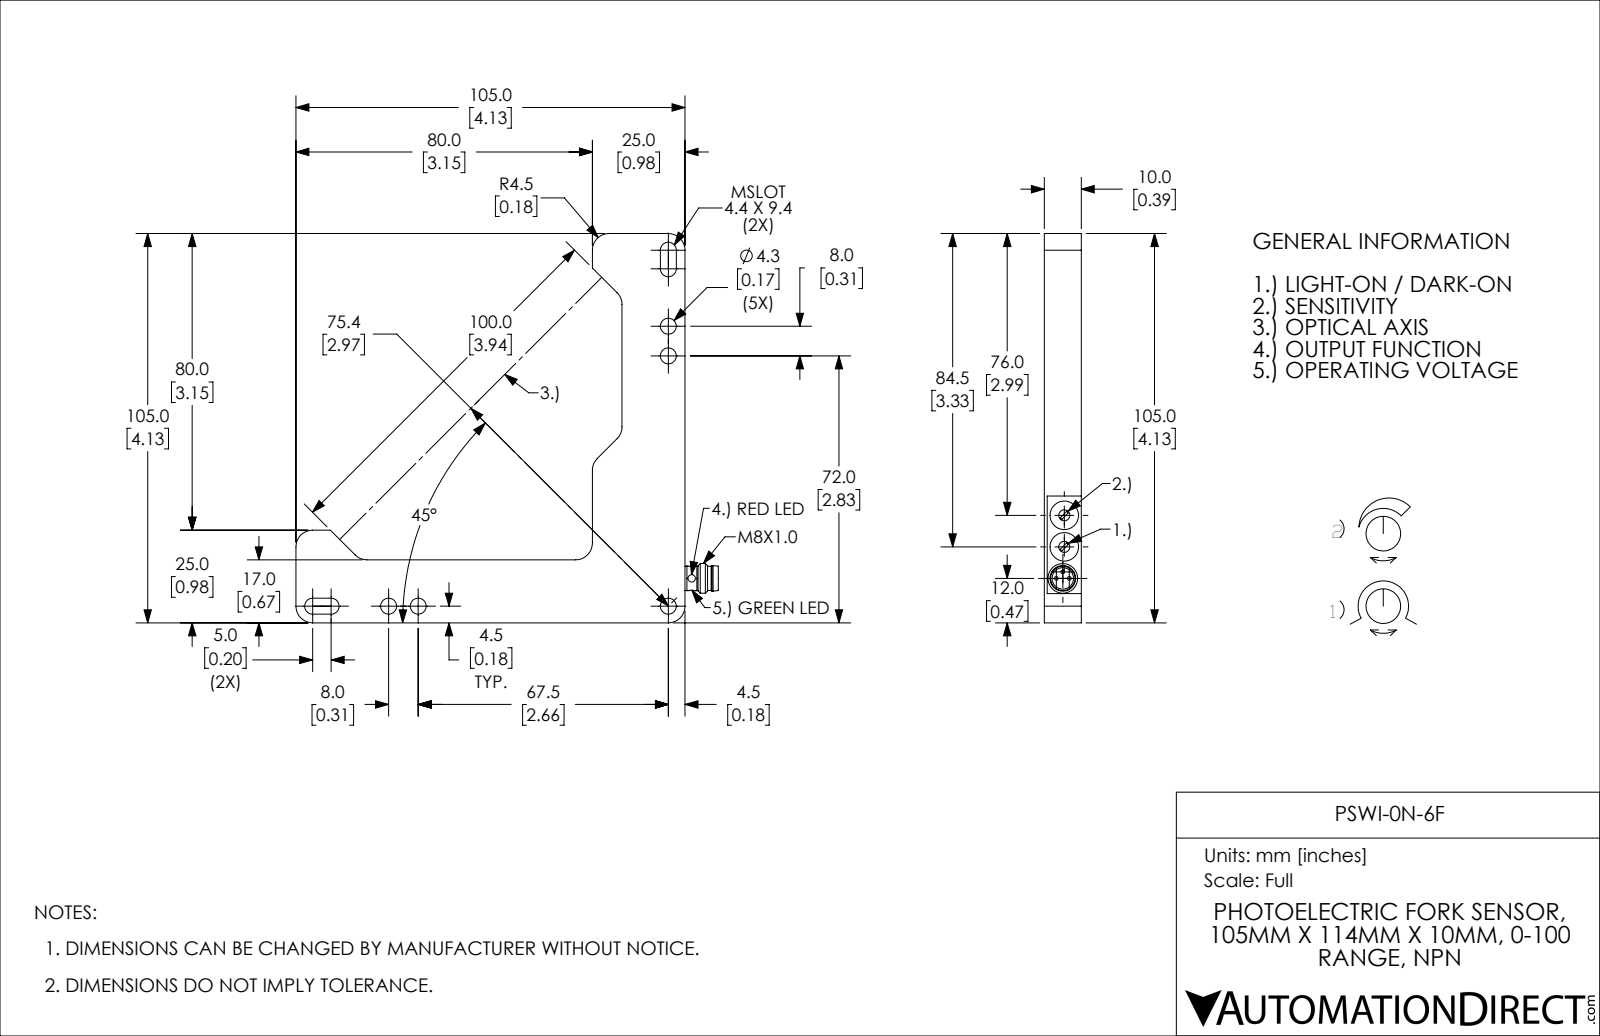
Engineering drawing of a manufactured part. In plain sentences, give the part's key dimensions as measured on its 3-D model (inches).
The part is named "PSWI-0N-6F". Its 3-D file was written by "SolidWorks 2017 (AUTOMOTIVE_DESIGN)". It is 1 solid with 90 faces: 42 planar, 41 cylindrical and 7 other. Overall it measures 4.488 by 4.134 by 0.394 inches. Its volume is 2.191 cubic inches and its surface area 20.03 square inches. Round holes: 5 of diameter 0.169, 2 of diameter 0.079, 2 of diameter 0.118, 2 of diameter 0.303, 1 of diameter 0.228. Round bosses or shafts: 3 of diameter 0.039, 1 of diameter 0.315, 1 of diameter 0.272, 1 of diameter 0.264, 1 of diameter 0.257. Partial cylindrical surfaces (rounded edges, fillets, slot ends): 10 of radius 0.177, 4 of radius 0.085, 2 of radius 0.049. The main face-to-face distances are 0.394, 0.669, 4.134, 3.465, 0.984, 0.315, 3.15, 4.13, 0.98, 0.665. The hole center spacings are 0.315, 2.657, 2.972, 3.987, 0.335, 0.335, 0.385, 0.669.
